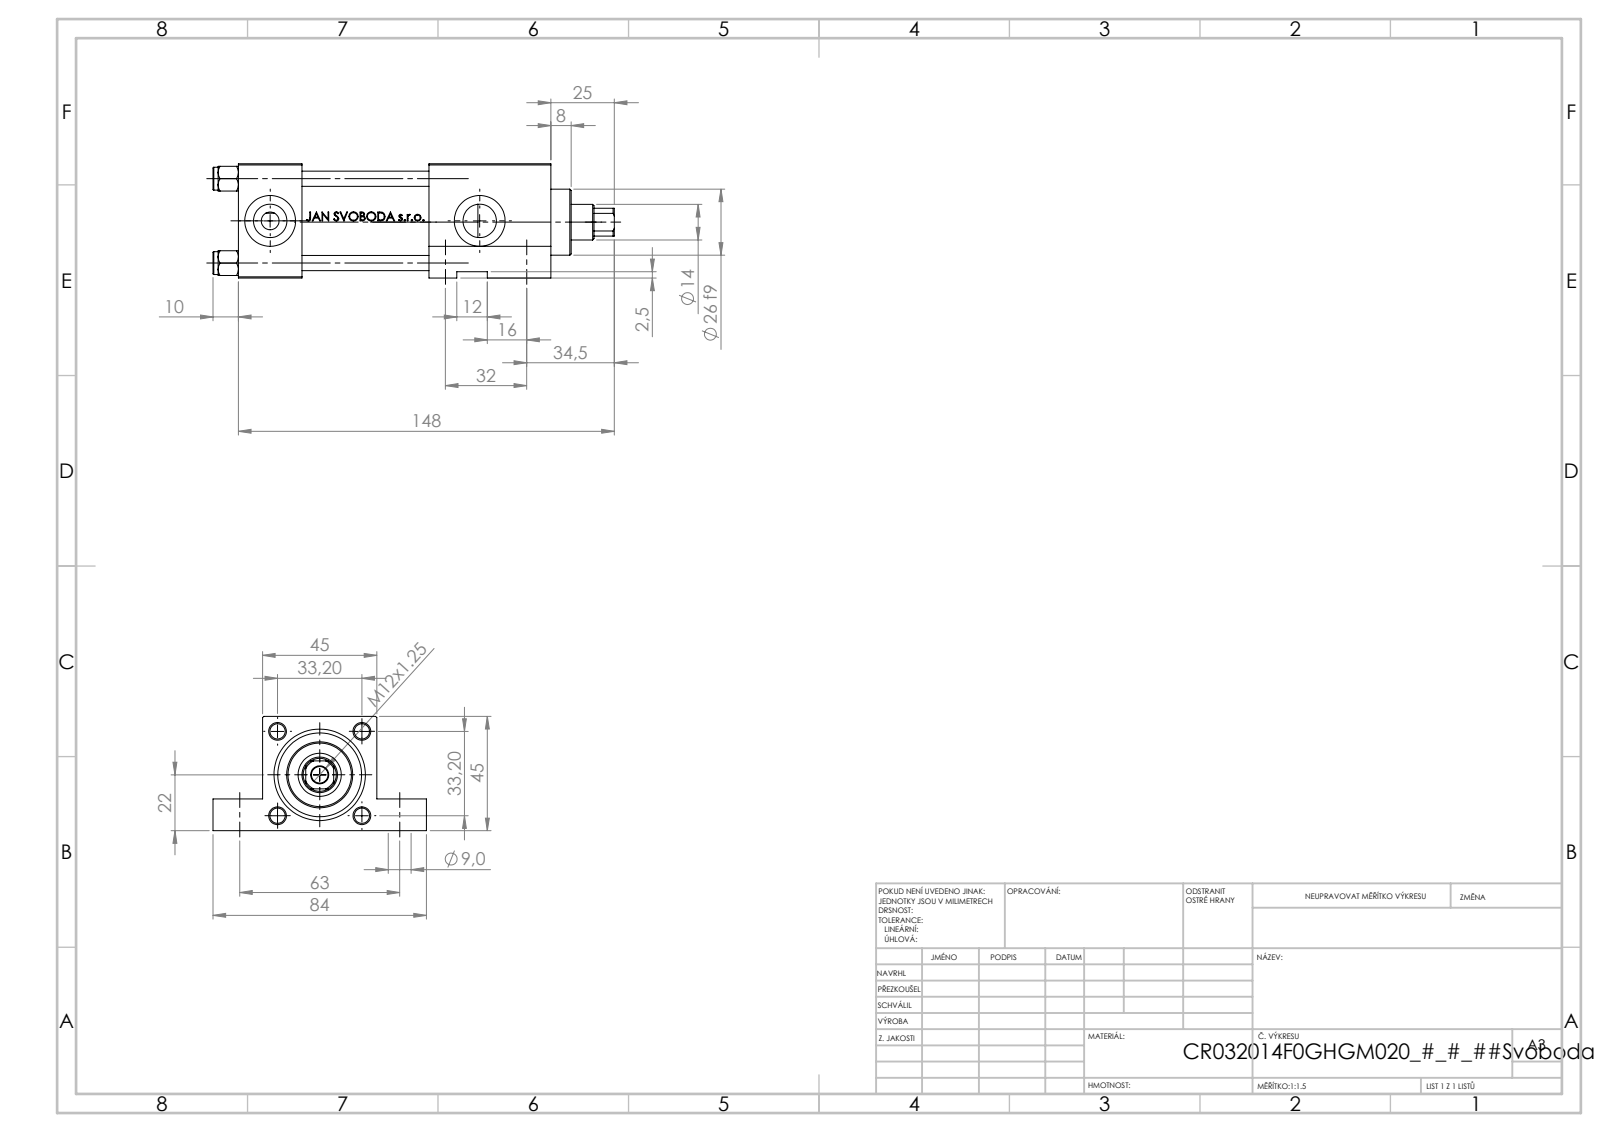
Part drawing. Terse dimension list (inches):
name: V215_VC_A; V215CR_F_TYCINKA; V215CR_VCP_F; V215CR_F_Body (+1 more)
written by: SolidWorks 2019 (CONFIG_CONTROL_DESIGN)
unit: in
bodies: 11 solids, 1102 faces (436 planar, 126 cylindrical, 540 other)
size: 6.22 × 3.307 × 1.772
volume: 12.95 in³; area: 112.5 in²
holes: 4× ⌀0.236, 4× ⌀0.354, 2× ⌀0.276, 2× ⌀0.518, 2× ⌀0.787, 1× ⌀0.256, 1× ⌀0.551, 1× ⌀0.669, 1× ⌀0.945, 1× ⌀1.26, 1× ⌀1.299
bosses: 4× ⌀0.354, 1× ⌀1.496, 1× ⌀1.024
rounds: 1× R0.256
face distances: 1.772, 0.984, 3.858, 4.843, 1.969, 1.28, 2.953, 1.89, 0.492, 0.394
hole spacings: 1.307, 0.911, 0.938, 1.26, 1.848, 2.48, 2.782, 3.248
